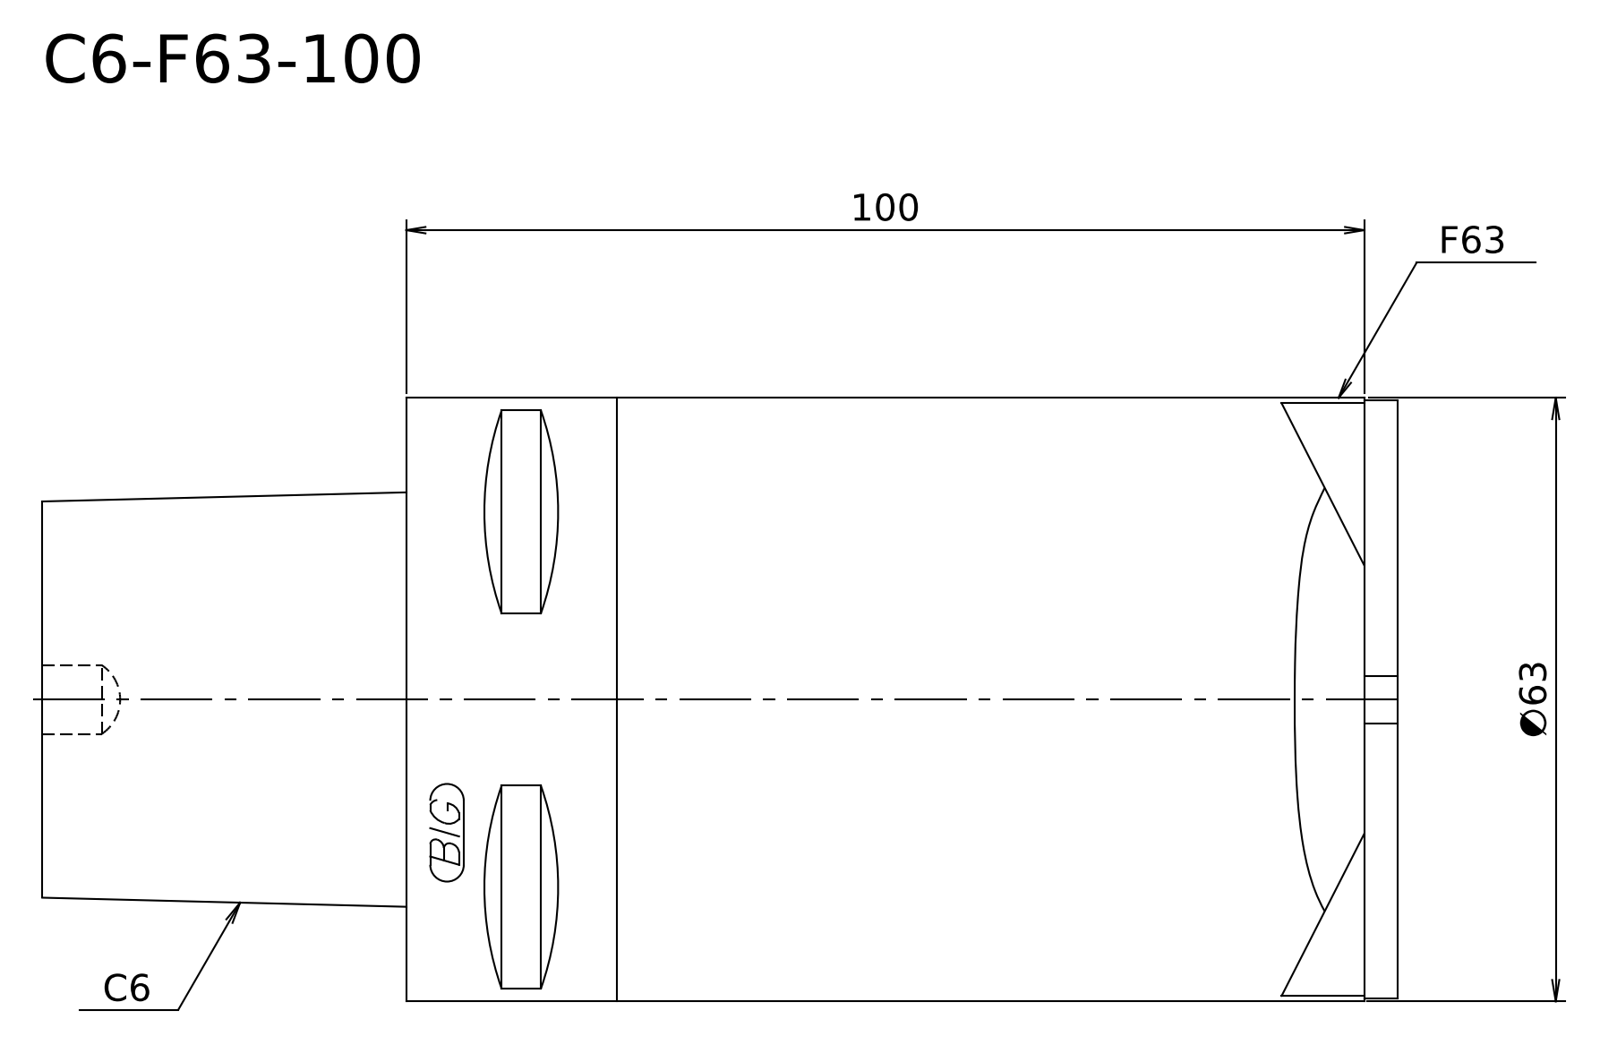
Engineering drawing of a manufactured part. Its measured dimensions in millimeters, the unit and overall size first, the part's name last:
Units: millimetres
Overall size (bounding box): 138 × 63 × 63
Round bosses / shafts (diameter × count): ⌀63 ×1
Main face-to-face distances: 100, 38, 138
Volume: 365 163 mm³ · Surface area: 30 953 mm²
Bodies: 1 solid, 7 faces (3 planar, 2 cylindrical, 2 other)
Part name (STEP PRODUCT): C6-F63-100
STEP written by: SolidWorks 2021 (CONFIG_CONTROL_DESIGN)
